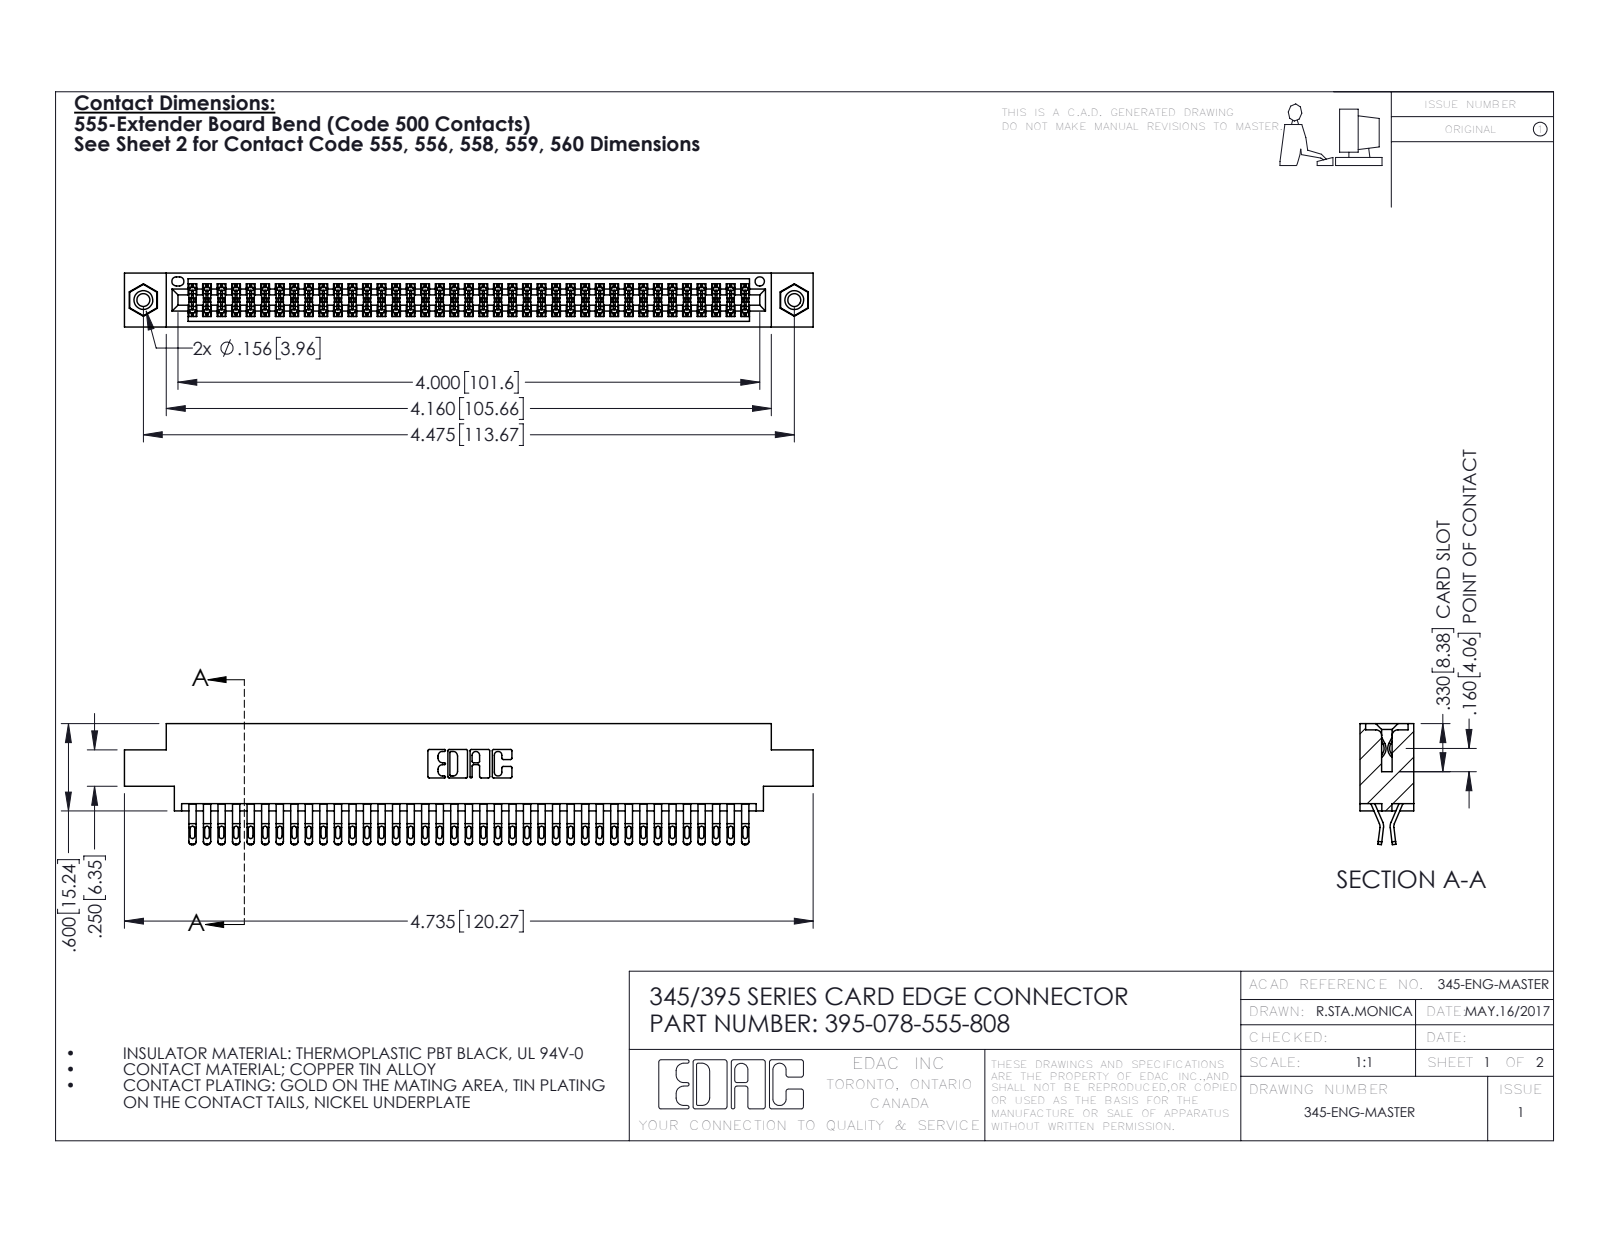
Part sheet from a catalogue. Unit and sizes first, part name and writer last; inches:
Units: inches
Overall size (bounding box): 4.735 × 0.832 × 0.37
Round holes (diameter × count): ⌀0.089 ×2, ⌀0.125 ×2, ⌀0.156 ×2, ⌀0.064 ×1
Round bosses / shafts (diameter × count): ⌀0.155 ×2
Partial cylindrical surfaces — rounded edges, fillets, slot ends (radius × count): R0.016 ×195, R0.02 ×156, R0.006 ×117, R0.01 ×22, R0.007 ×6, R0.031 ×6, R0.026 ×3, R0.01 ×2
Main face-to-face distances: 0.072, 0.298, 0.37, 0.025, 0.2, 0.098, 0.272, 0.225, 0.175, 0.149
Hole centre spacings: 0.27, 4.239, 4.475
Volume: 0.718 in³ · Surface area: 28.32 in²
Bodies: 81 solids, 4558 faces (2534 planar, 2008 cylindrical, 16 other)
Part name (STEP PRODUCT): 345-292-001_555 Tail; 395-078-555-808; 345 Part_0.170 Offset - 0.156 Dia-TI; 345-250-001_345-250-003-102
STEP written by: SolidWorks 2016 (CONFIG_CONTROL_DESIGN)
